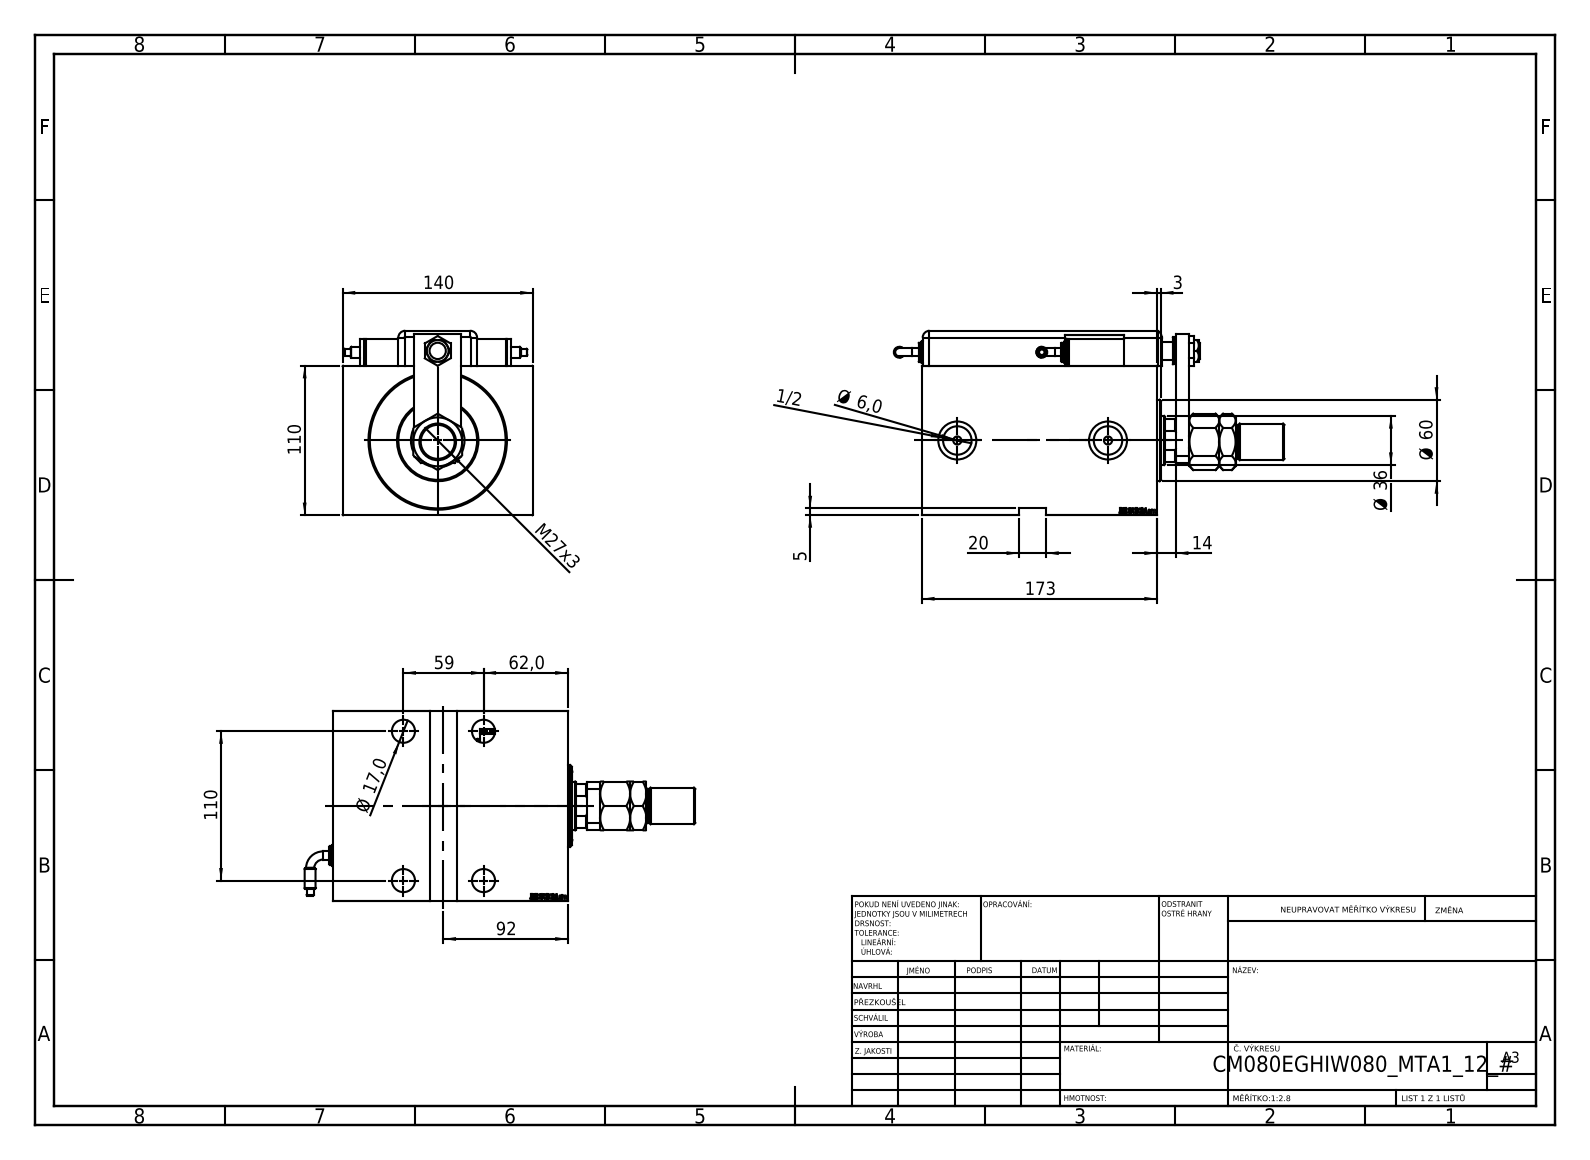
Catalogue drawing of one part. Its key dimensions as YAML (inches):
part_name: "V450CM_E_Body; SWITCH Q; NUT_D13; ZARAZKA_Q (+7 more)"
step_written_by: "SolidWorks 2019 (CONFIG_CONTROL_DESIGN)"
units: inches
bodies: {solids: 14, faces: 1317, planar: 635, cylindrical: 119, other: 563}
overall_size: [11.329, 5.512, 5.346]
volume: 149.7
surface_area: 511
round_holes:
  - {diameter: 0.669, count: 4}
  - {diameter: 0.984, count: 4}
  - {diameter: 0.157, count: 2}
  - {diameter: 0.236, count: 2}
  - {diameter: 0.315, count: 2}
  - {diameter: 0.825, count: 2}
  - {diameter: 1.102, count: 2}
  - {diameter: 0.472, count: 1}
  - {diameter: 0.512, count: 1}
  - {diameter: 0.551, count: 1}
  - {diameter: 1.004, count: 1}
  - {diameter: 1.063, count: 1}
round_bosses_or_shafts:
  - {diameter: 0.787, count: 3}
  - {diameter: 0.63, count: 2}
  - {diameter: 0.551, count: 2}
  - {diameter: 0.315, count: 2}
  - {diameter: 0.236, count: 2}
  - {diameter: 0.198, count: 2}
  - {diameter: 3.228, count: 1}
  - {diameter: 2.362, count: 1}
partial_cylinders:
  - {radius: 0.197, count: 9}
  - {radius: 0.394, count: 1}
  - {radius: 0.689, count: 1}
face_to_face_distances: [4.331, 5.512, 0.118, 6.811, 0.827, 5.984, 0.197, 5.346, 1.016, 2.283]
hole_center_spacings: [2.323, 2.798, 3.352, 4.331, 4.825, 4.914, 5.167, 0.039]
